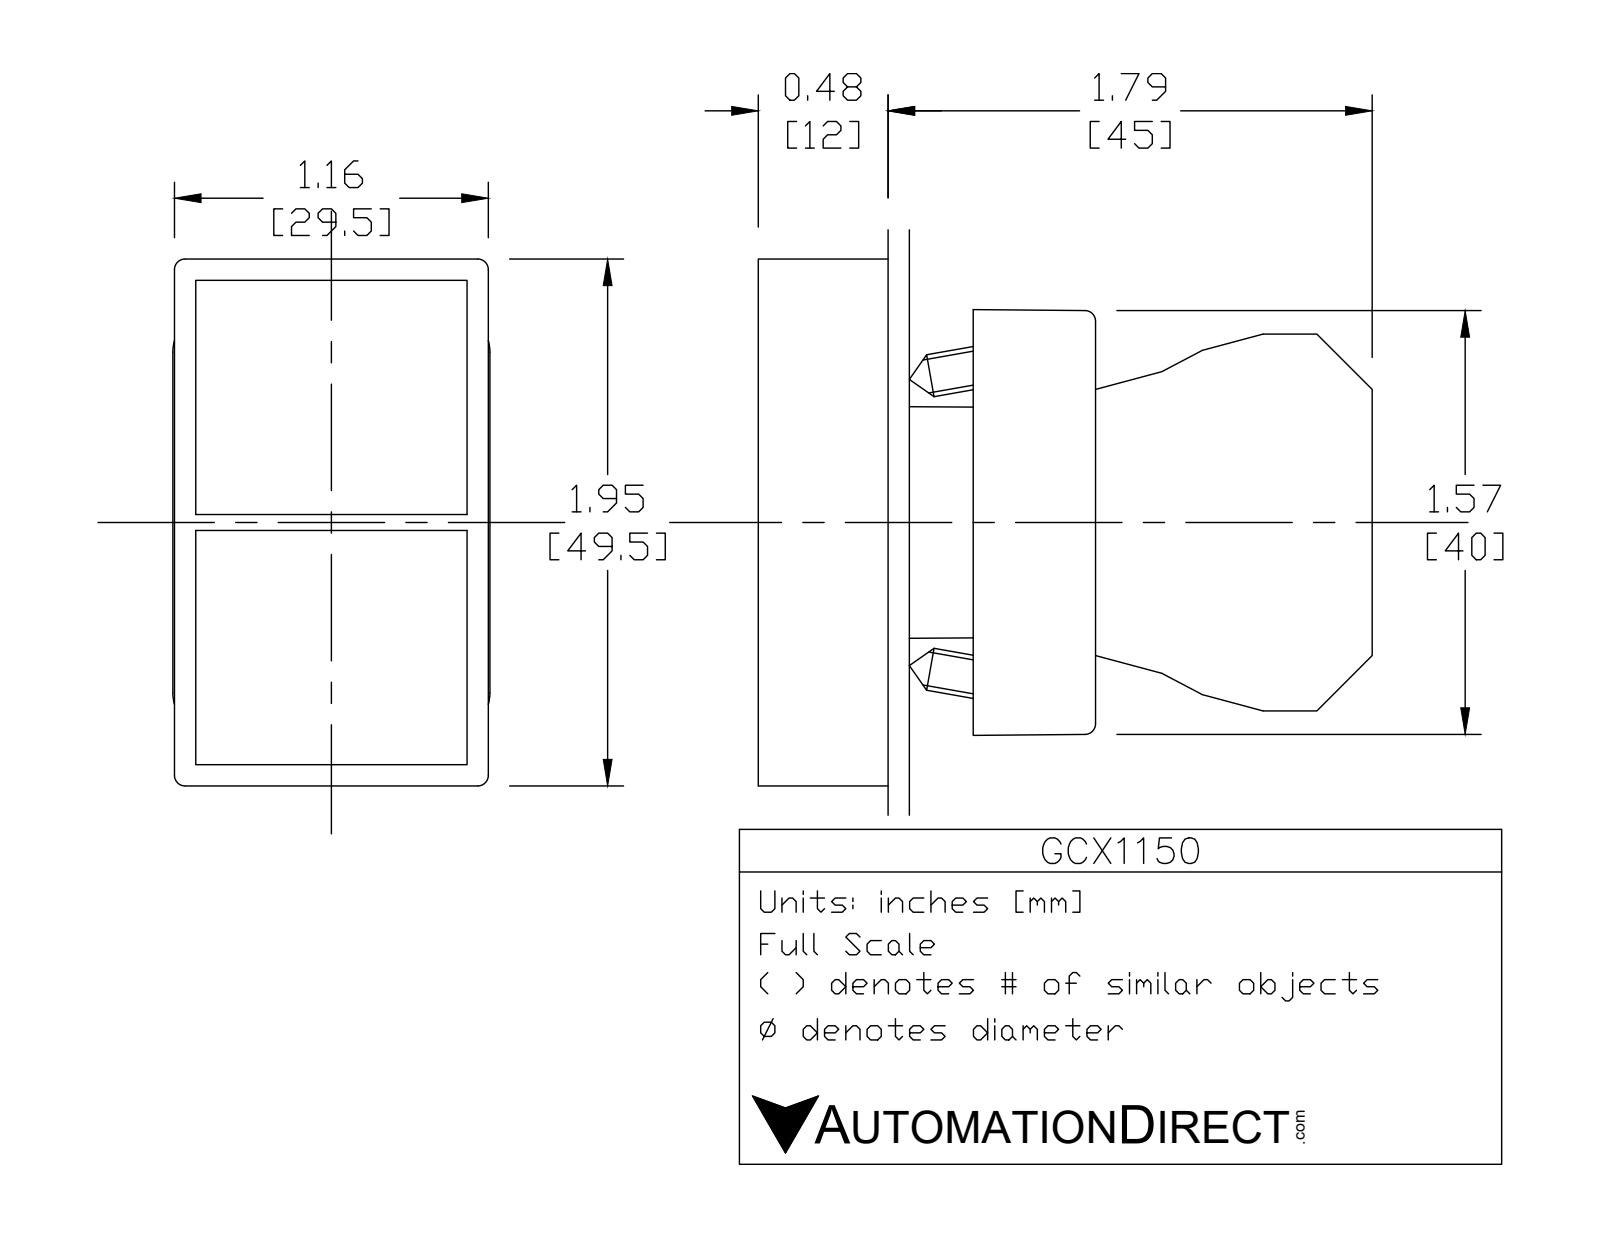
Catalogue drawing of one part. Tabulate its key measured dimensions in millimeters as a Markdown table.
| quantity | value |
| --- | --- |
| part name | ecx1030; ecx1029; ecx1040; GCX1150 OPERATOR (+1 more) |
| STEP written by | SolidWorks 2016 (AUTOMOTIVE_DESIGN) |
| units | millimeters |
| bodies | 8 solids, 484 faces (315 planar, 140 cylindrical, 29 other) |
| overall size | 56.3 × 49.5 × 29.9 |
| volume | 47 950 mm³ |
| surface area | 27 680 mm² |
| round holes (diameter × count) | 2 × 4, 2.2 × 2, 3.1 × 2, 3.3 × 2, 5 × 1, 22.3 × 1, 22.6 × 1 |
| round bosses / shafts (diameter × count) | 4 × 2, 24 × 1, 21.7 × 1, 19.8 × 1 |
| partial cylindrical surfaces (radius × count) | 1.5 × 24, 1 × 12, 3.1 × 12, 4 × 12, 1 × 4, 1.6 × 2, 2 × 2, 3.3 × 2 |
| main face-to-face distances | 0.5, 1, 13.5, 1.5, 14.7, 15.2, 15, 18.8, 30.3, 11.5 |
| hole center spacings | 6, 13.8, 25.6, 24.9, 12, 12.4, 27.6 |
